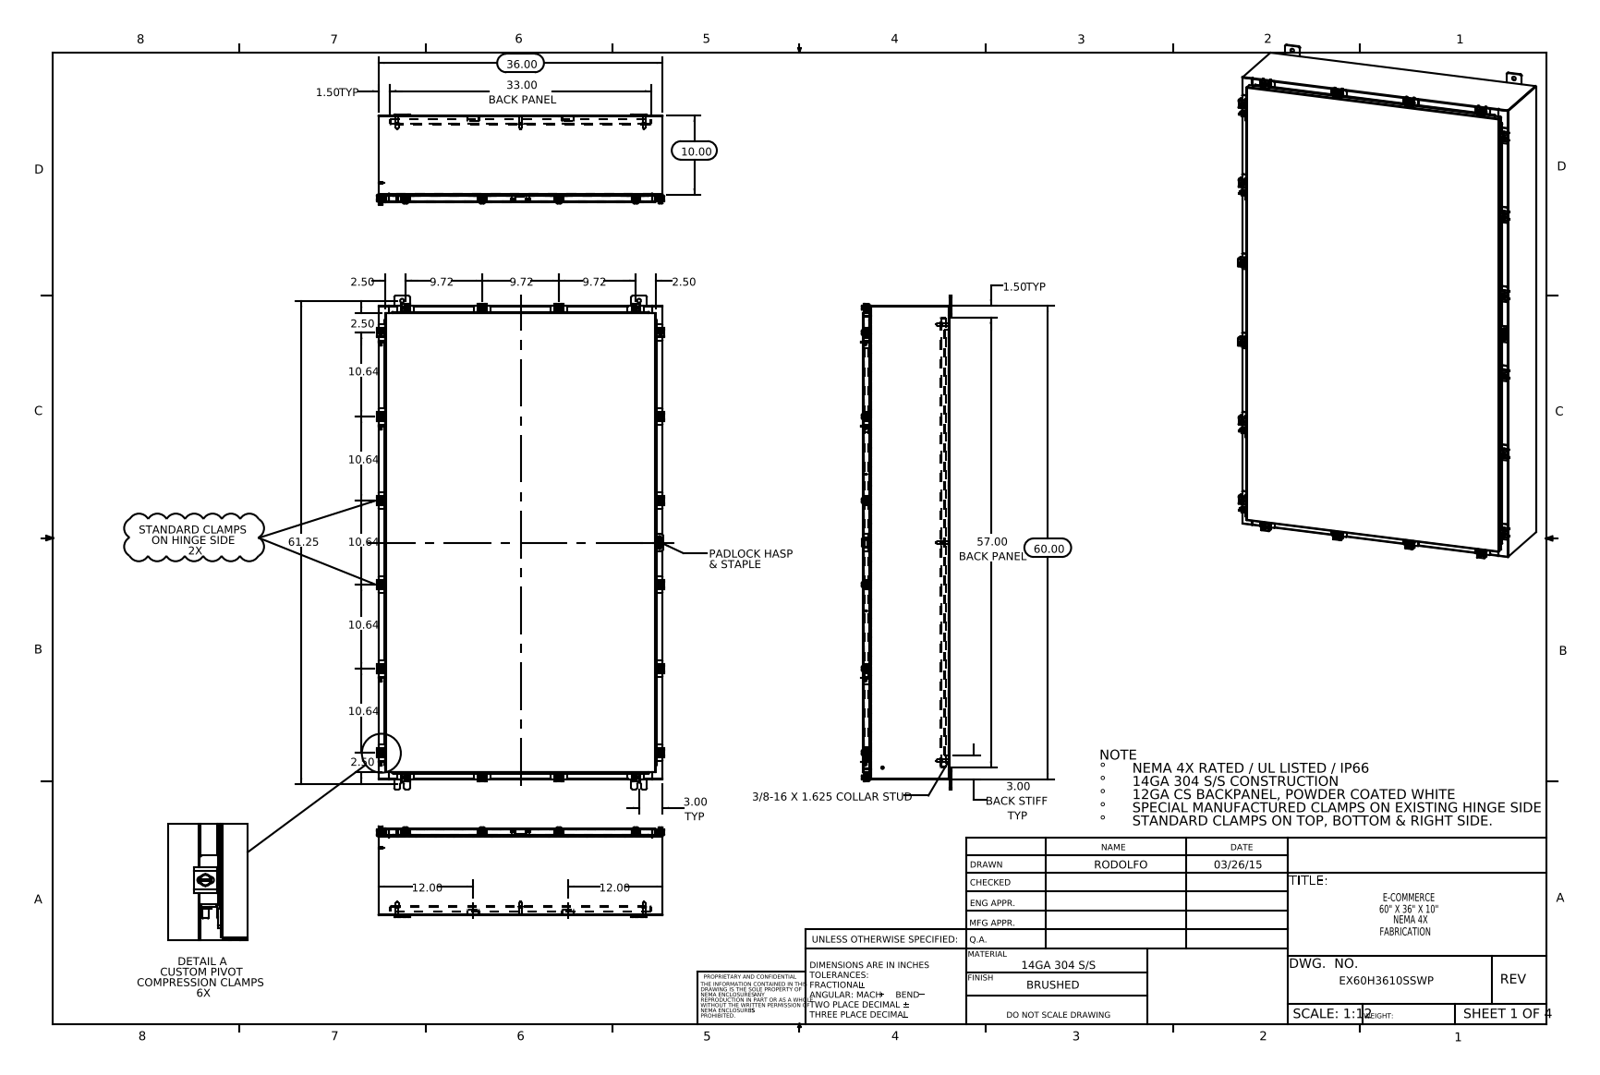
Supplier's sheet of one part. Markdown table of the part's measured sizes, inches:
| quantity | value |
| --- | --- |
| part name | EX60H3610SSWP Mounting Studs; ATEX CLAMP HINGE BRAKET; EX60H3610SSWP Cover; EX60H3610SSWP Backpanel (+8 more) |
| STEP written by | SolidWorks 2014 (CONFIG_CONTROL_DESIGN) |
| units | inches |
| bodies | 140 solids, 3424 faces (1773 planar, 1319 cylindrical, 332 other) |
| overall size | 62.5 × 36.421 × 11.453 |
| volume | 764.2 in³ |
| surface area | 18 917 in² |
| round holes (diameter × count) | 0.213 × 20, 0.26 × 20, 0.5 × 12, 0.25 × 9, 0.125 × 1 |
| round bosses / shafts (diameter × count) | 0.5 × 20, 0.25 × 20, 0.399 × 16, 0.625 × 8, 0.375 × 8, 0.33 × 8, 0.157 × 8, 0.14 × 8 |
| partial cylindrical surfaces (radius × count) | 0.06 × 84, 0.141 × 40, 0.013 × 38, 0.12 × 36, 0.088 × 34, 0.09 × 32, 0.05 × 29, 0.145 × 28 |
| main face-to-face distances | 0.075, 10.9, 10.826, 0.104, 10.975, 1, 1.075, 9.826, 9.9, 1.179 |
| hole center spacings | 1.969, 2.224, 2.347, 13.972, 14.729, 16.126, 27.625, 29.744 |
